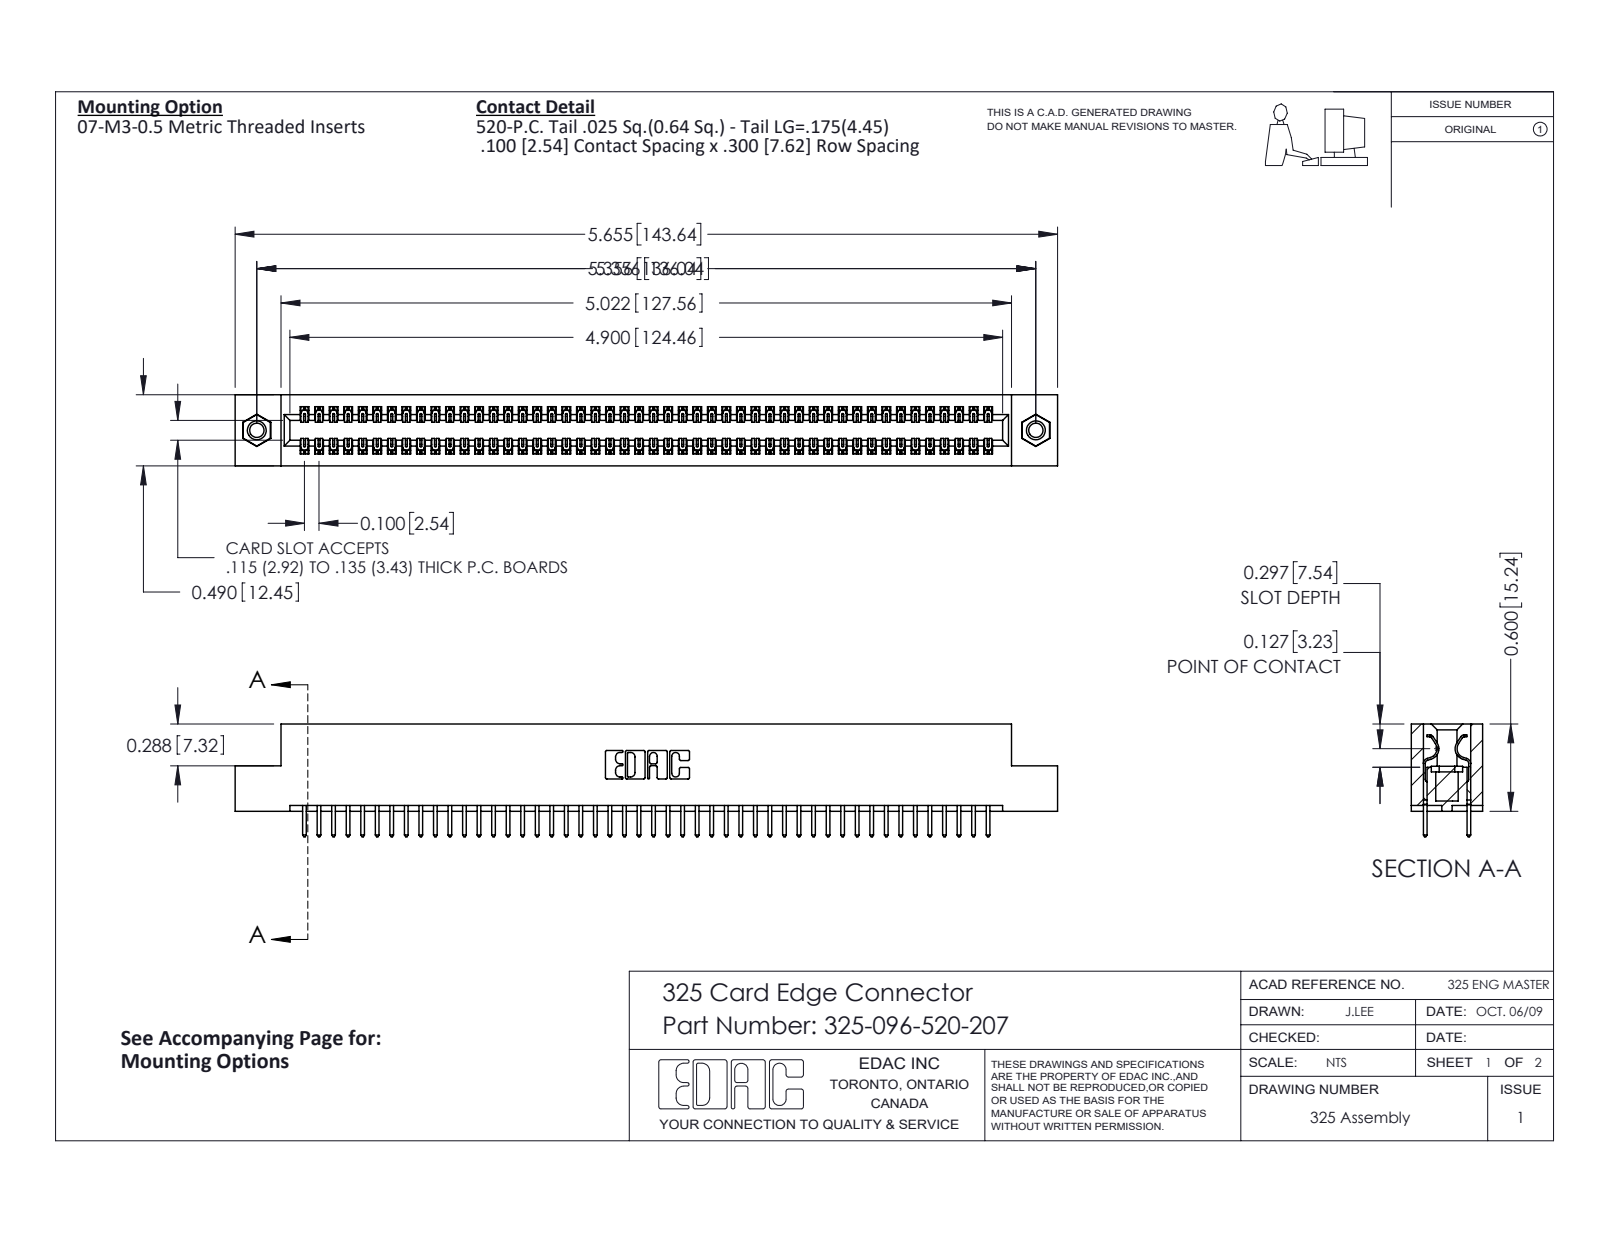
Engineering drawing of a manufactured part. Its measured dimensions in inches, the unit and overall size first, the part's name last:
Units: inches
Overall size (bounding box): 5.655 × 0.775 × 0.49
Round holes (diameter × count): ⌀0.098 ×2, ⌀0.125 ×2, ⌀0.16 ×2
Round bosses / shafts (diameter × count): ⌀0.155 ×2
Partial cylindrical surfaces — rounded edges, fillets, slot ends (radius × count): R0.006 ×144, R0.01 ×96, R0.01 ×22, R0.007 ×6, R0.031 ×6, R0.026 ×3, R0.014 ×2, R0.022 ×2
Main face-to-face distances: 0.083, 0.407, 0.3, 0.49, 0.107, 0.383, 0.025, 0.325, 0.275, 0.56
Hole centre spacings: 5.356
Volume: 1.133 in³ · Surface area: 34.8 in²
Bodies: 99 solids, 5166 faces (3558 planar, 1592 cylindrical, 16 other)
Part name (STEP PRODUCT): 345-250-001_345-250-005-103; 325-292-001_325-293-120; 325 Part_TI; 325-096-520-207
STEP written by: SolidWorks 2016 (CONFIG_CONTROL_DESIGN)
